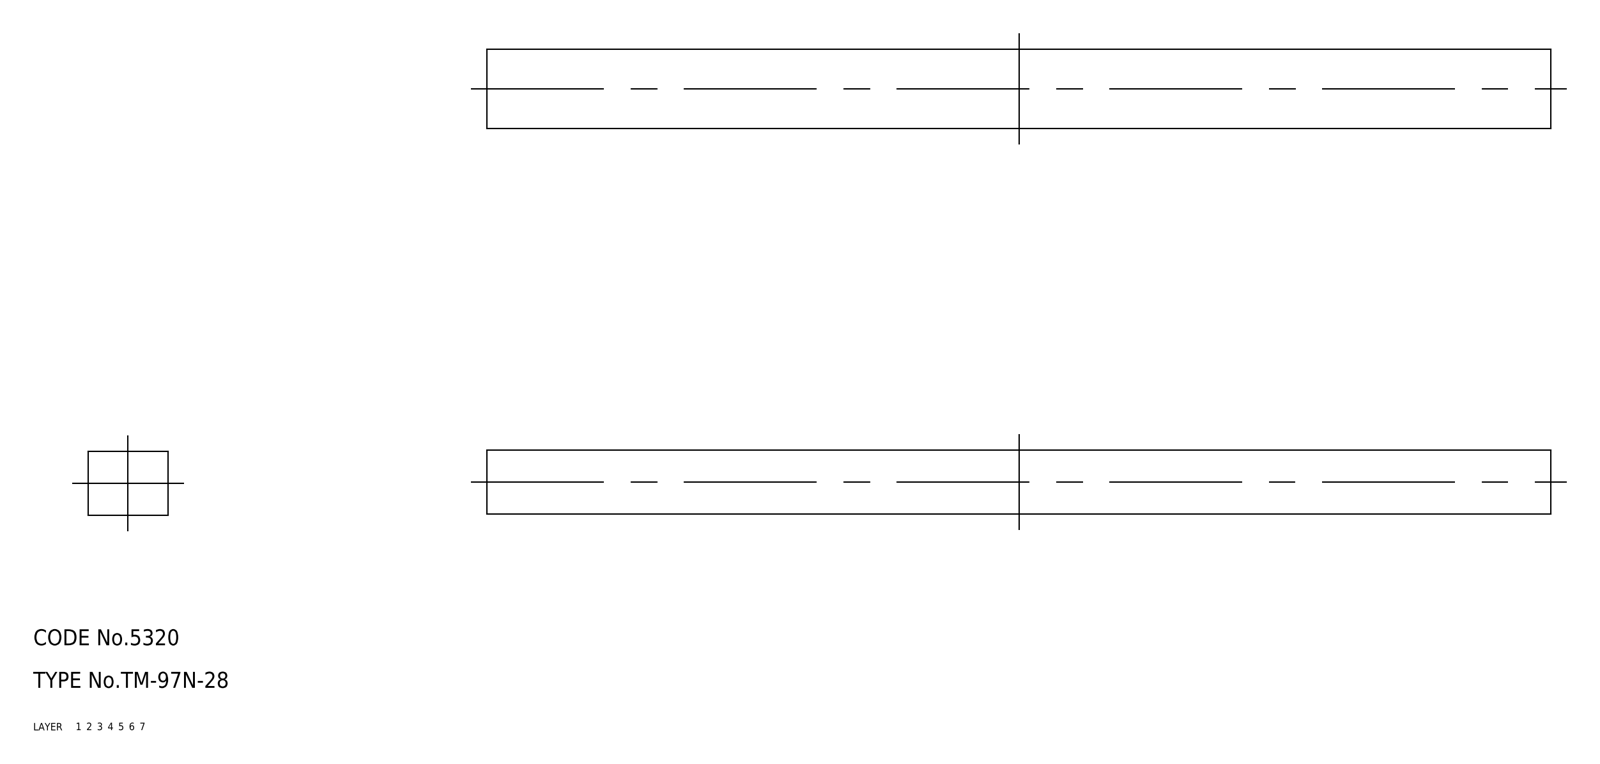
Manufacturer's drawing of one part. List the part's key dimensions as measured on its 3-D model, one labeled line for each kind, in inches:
Part name (STEP PRODUCT): rubber foam
STEP written by: CADfix (AUTOMOTIVE_DESIGN)
Units: inches
Bodies: 1 solid, 6 faces (0 planar, 0 cylindrical, 6 other)
Overall size (bounding box): 7.874 × 0.591 × 0.472
Volume: 2.197 in³ · Surface area: 17.3 in²
